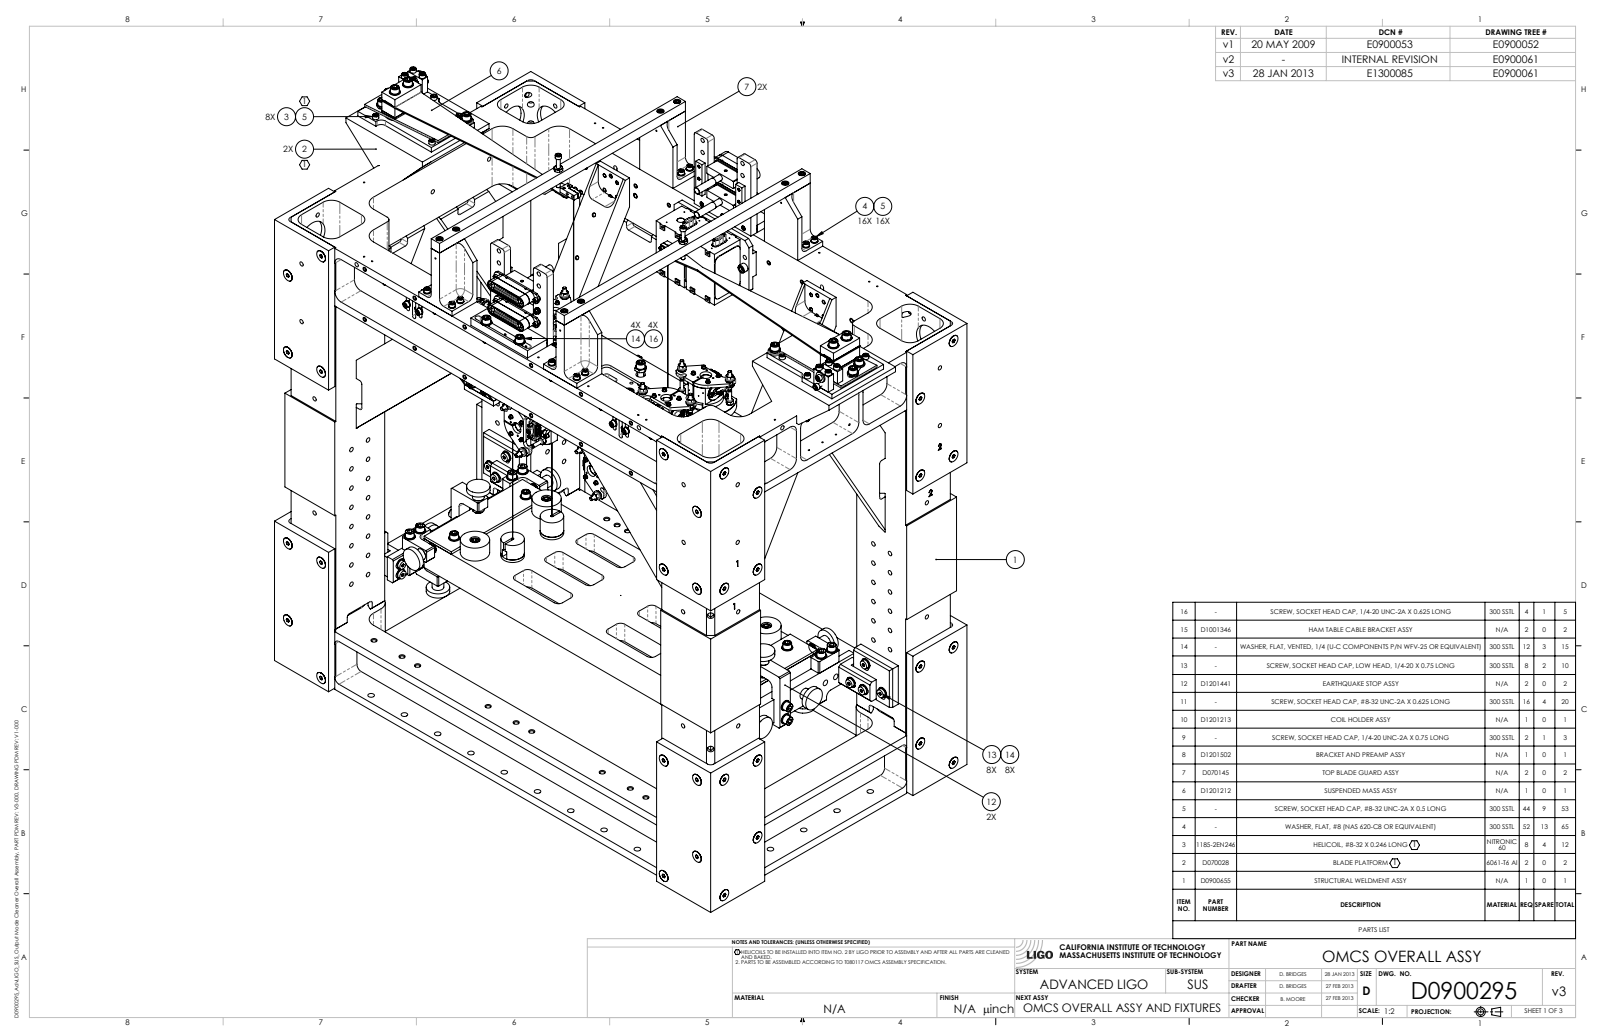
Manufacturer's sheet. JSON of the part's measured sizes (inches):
{"part_name": "SST_HexNut_HN No. 4; NAS 620 FLAT WASHERS_________ FLAT WASHERS NAS 620-C416L (1-4) (OR EQUIV.); D070027_AdLIGO_SUS_OMC_SUS-METAL-DUMMY-OPTICAL-BENCH_counterboars no mass; SST_setscrew_0.5-20 Set Screw X 2 LONG (+8 more)", "step_written_by": "SolidWorks 2013 (CONFIG_CONTROL_DESIGN)", "units": "inches", "bodies": {"solids": 1440, "faces": 30219, "planar": 11472, "cylindrical": 12913, "other": 5834}, "overall_size": [29.471, 27.133, 15.432], "volume_in3": 915.1, "surface_area_in2": 6987, "round_holes": [[0.136, 132], [0.213, 128], [0.201, 114], [0.04, 100], [0.056, 100], [0.067, 100], [0.089, 98], [0.266, 94], [0.164, 72], [0.169, 68], [0.02, 54], [0.115, 46]], "round_bosses_or_shafts": [[0.25, 160], [0.075, 100], [0.064, 100], [0.112, 94], [0.183, 88], [0.266, 74], [0.304, 68], [0.14, 60]], "partial_cylinders_radius": [[0.25, 104], [0.022, 100], [0.05, 88], [0.02, 66], [0.015, 64], [0.125, 54], [0.375, 44], [0.094, 28]], "face_to_face_distances": [0.25, 1.435, 2.75, 2.937, 3, 2.687, 1.502, 13.219, 0.187, 2.5], "hole_center_spacings": [1, 2, 6, 4, 13.937, 14.142, 14.56, 1.414]}
